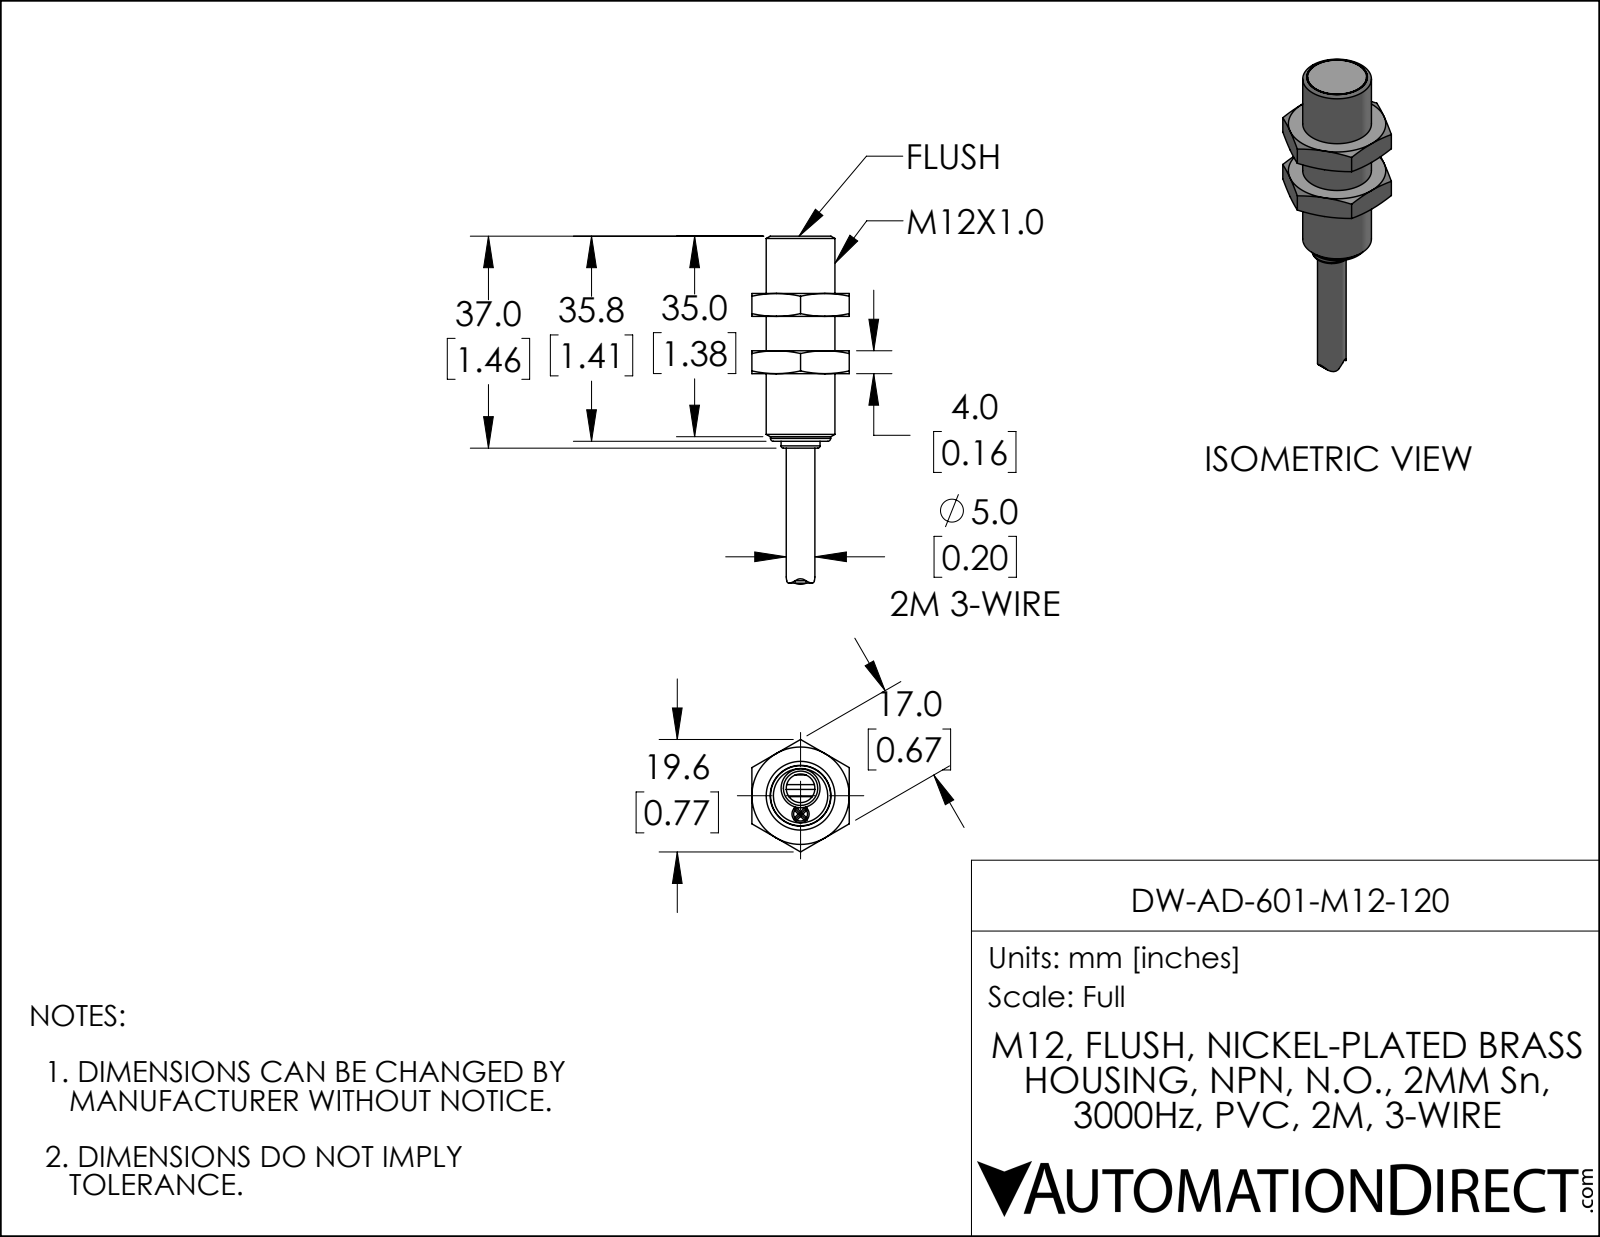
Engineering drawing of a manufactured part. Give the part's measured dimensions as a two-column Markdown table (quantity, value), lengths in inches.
| quantity | value |
| --- | --- |
| part name | DW-AD-601-M12-120 |
| STEP written by | SolidWorks 2019 (AUTOMOTIVE_DESIGN) |
| units | inches |
| bodies | 1 solid, 81 faces (34 planar, 14 cylindrical, 33 other) |
| overall size | 2.392 × 0.773 × 0.669 |
| volume | 0.342 in³ |
| surface area | 4.072 in² |
| round holes (diameter × count) | 0.415 × 1 |
| round bosses / shafts (diameter × count) | 0.472 × 1, 0.413 × 1, 0.406 × 1, 0.268 × 1, 0.197 × 1, 0.118 × 1 |
| partial cylindrical surfaces (radius × count) | 0.031 × 1, 0.041 × 1, 0.165 × 1, 0.248 × 1, 0.331 × 1 |
| main face-to-face distances | 0.394, 0.157, 0.669, 0.551, 0.236, 0.787, 0.945, 1.409, 1.016, 0.858 |
